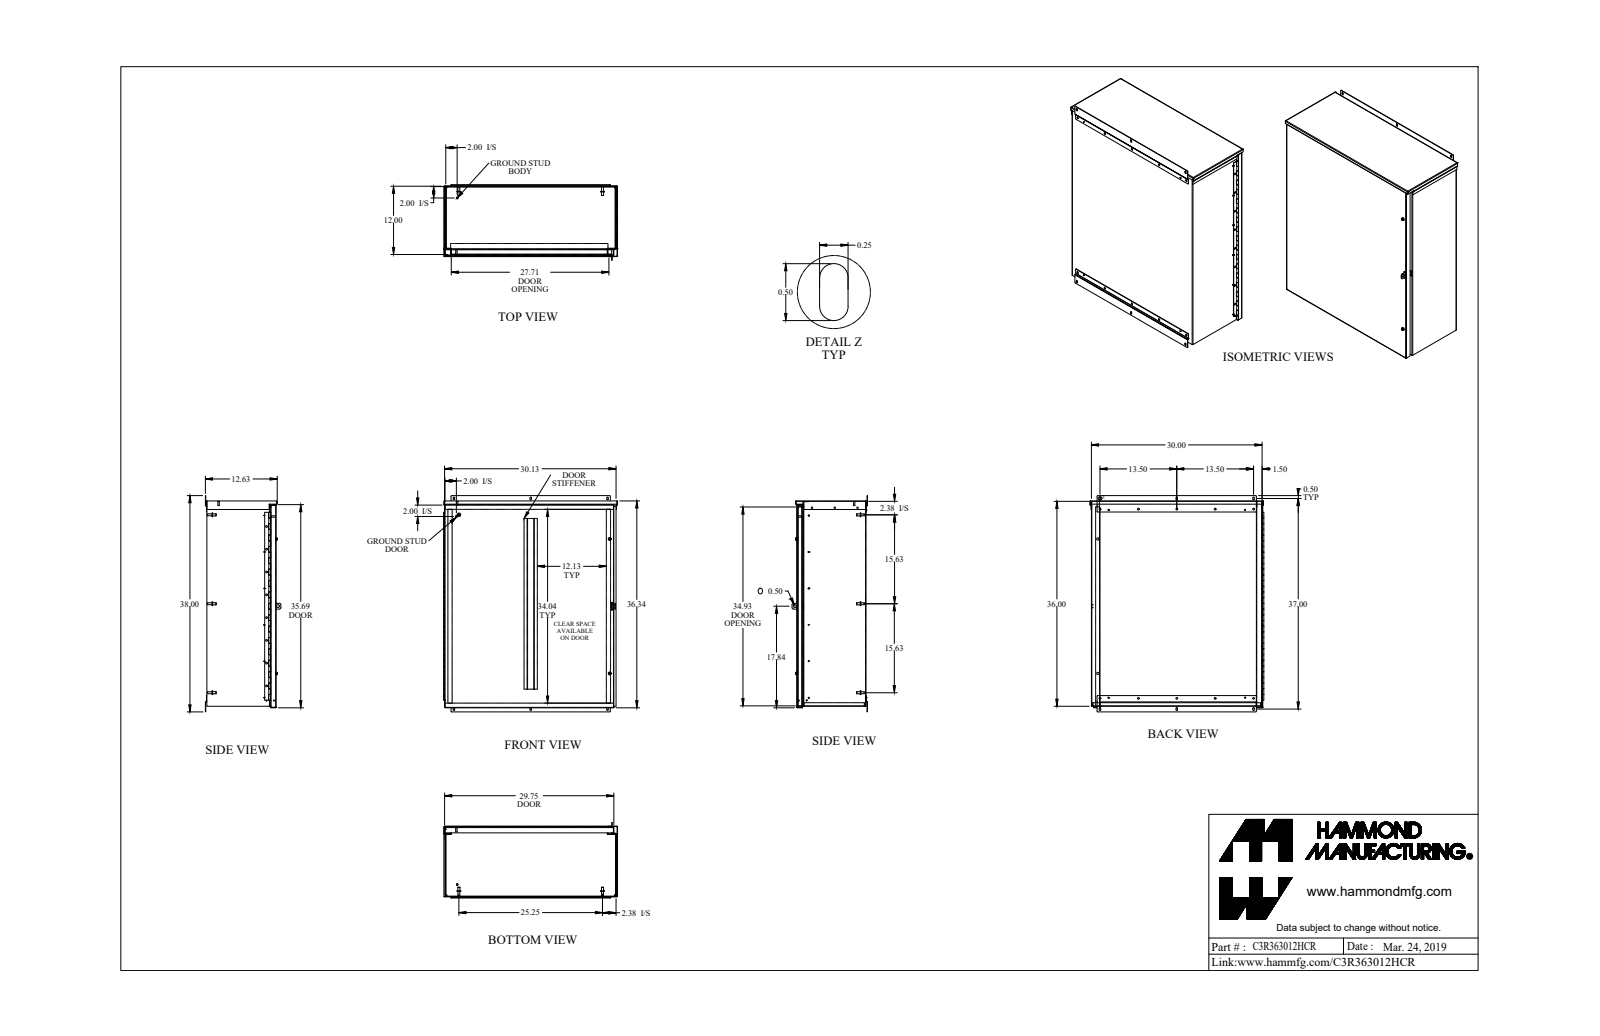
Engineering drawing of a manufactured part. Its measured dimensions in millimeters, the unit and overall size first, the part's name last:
Units: millimetres
Overall size (bounding box): 965.2 × 776.5 × 336.8
Round holes (diameter × count): ⌀7.9 ×10, ⌀7.7 ×8, ⌀3.5 ×4, ⌀3.6 ×4, ⌀6.4 ×3, ⌀6.6 ×3, ⌀8 ×3, ⌀6.8 ×2, ⌀7.1 ×2, ⌀7.4 ×2, ⌀10.1 ×2, ⌀4.8 ×1
Round bosses / shafts (diameter × count): ⌀3.3 ×12, ⌀16.5 ×6, ⌀9.5 ×6, ⌀8.4 ×6, ⌀13 ×3, ⌀6.2 ×3, ⌀4.7 ×3, ⌀12.7 ×2
Partial cylindrical surfaces — rounded edges, fillets, slot ends (radius × count): R0.9 ×39, R2.7 ×39, R3.2 ×23, R4.3 ×3, R6.4 ×2
Main face-to-face distances: 1.8, 307.3, 309.2, 305.5, 760.2, 914.4, 762, 758.3, 912.6, 916.2
Hole centre spacings: 101.6, 171.5, 203.2, 861.8, 342.9, 304.8, 911.5, 38.2
Volume: 5 703 000 mm³ · Surface area: 6 121 000 mm²
Bodies: 37 solids, 1130 faces (601 planar, 459 cylindrical, 70 other)
Part name (STEP PRODUCT): C3R363012HCR_Default
STEP written by: SolidWorks 2019 (CONFIG_CONTROL_DESIGN)
